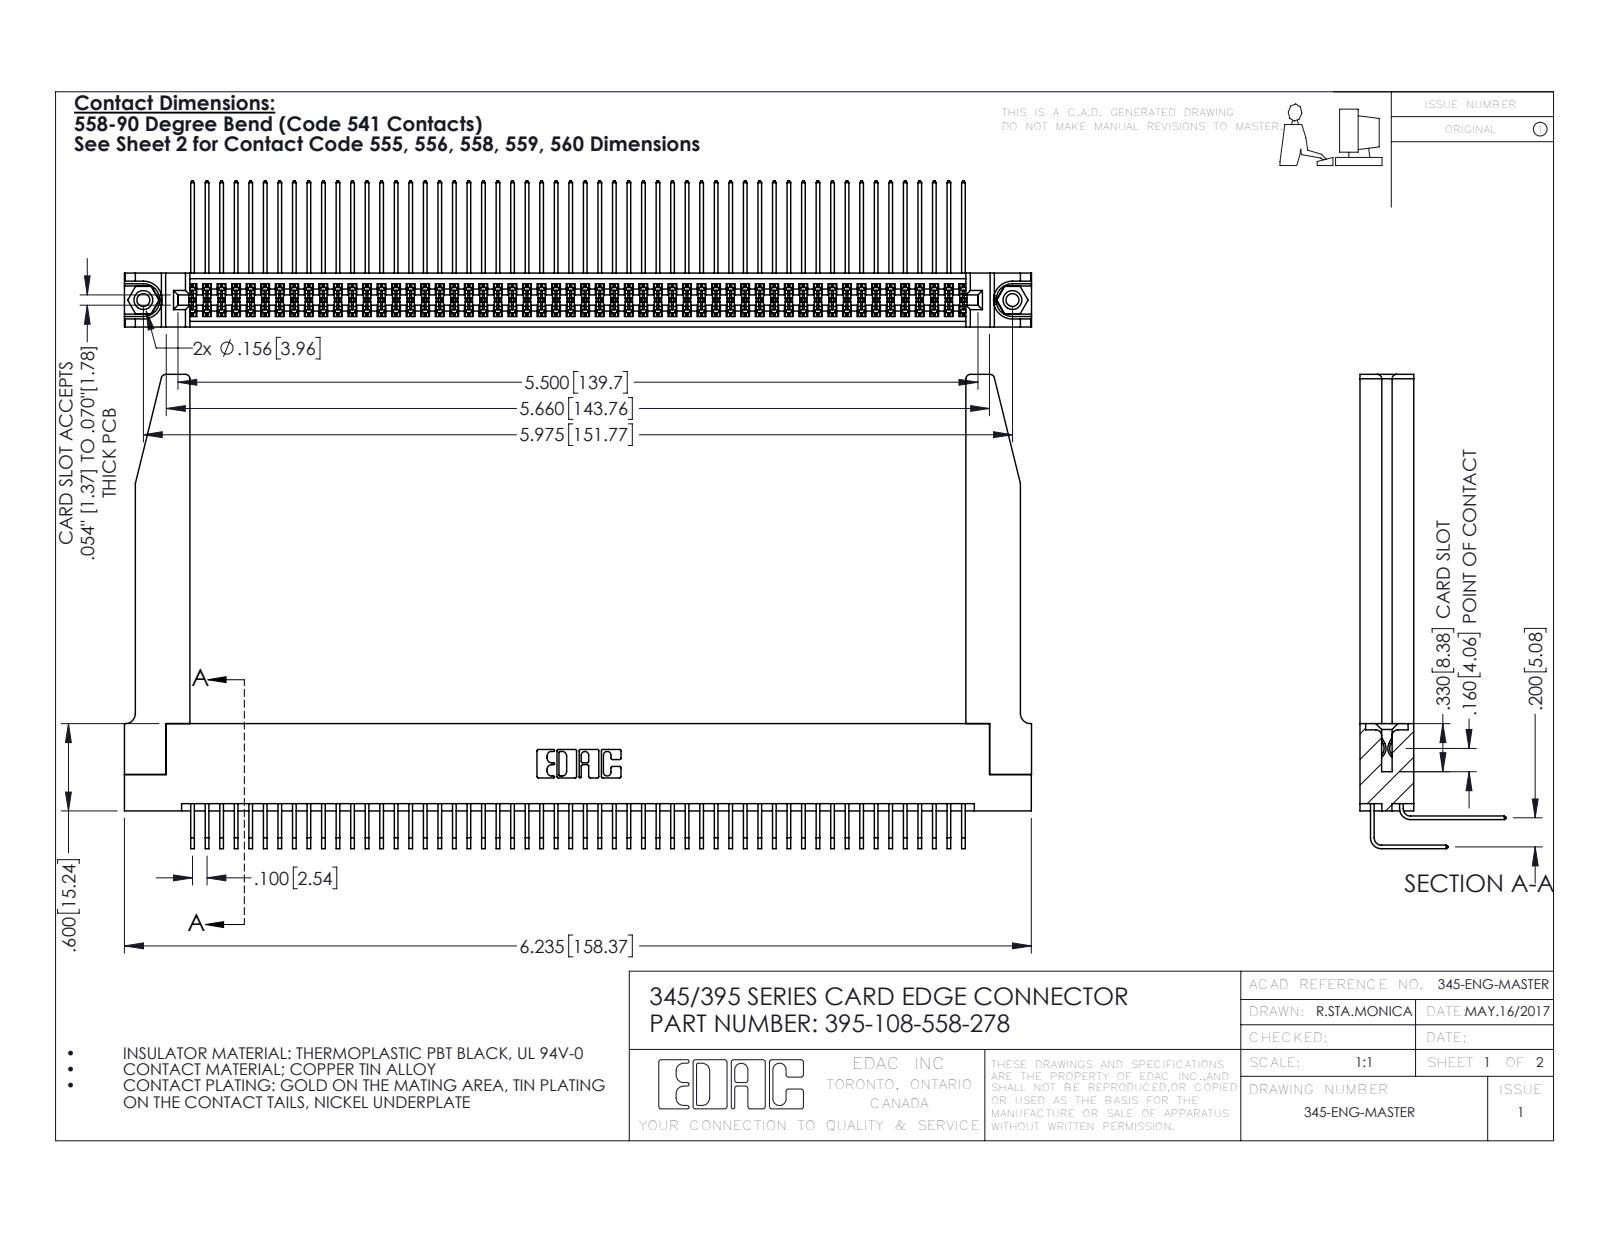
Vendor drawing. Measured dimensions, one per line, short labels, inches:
name: 345-220-078_345-220-078; 345-292-001_558 Tail - 2; 345-292-001_558 559 Tail - 1; 345 Part_Flush Mounting Lugs - 0.156 Dia-TH (+2 more)
written by: SolidWorks 2016 (CONFIG_CONTROL_DESIGN)
unit: in
bodies: 113 solids, 5976 faces (4002 planar, 1922 cylindrical, 52 other)
size: 6.236 × 3.259 × 1.005
volume: 1.458 in³; area: 52.44 in²
holes: 2× ⌀0.089, 2× ⌀0.125, 2× ⌀0.156, 1× ⌀0.064
bosses: 2× ⌀0.155
rounds: 163× R0.006, 22× R0.01, 8× R0.03, 6× R0.007, 6× R0.031, 3× R0.026, 2× R0.014, 2× R0.019
face distances: 0.072, 0.298, 0.37, 0.2, 0.098, 0.272, 0.025, 0.225, 0.285, 0.025
hole spacings: 0.27, 5.739, 5.975
